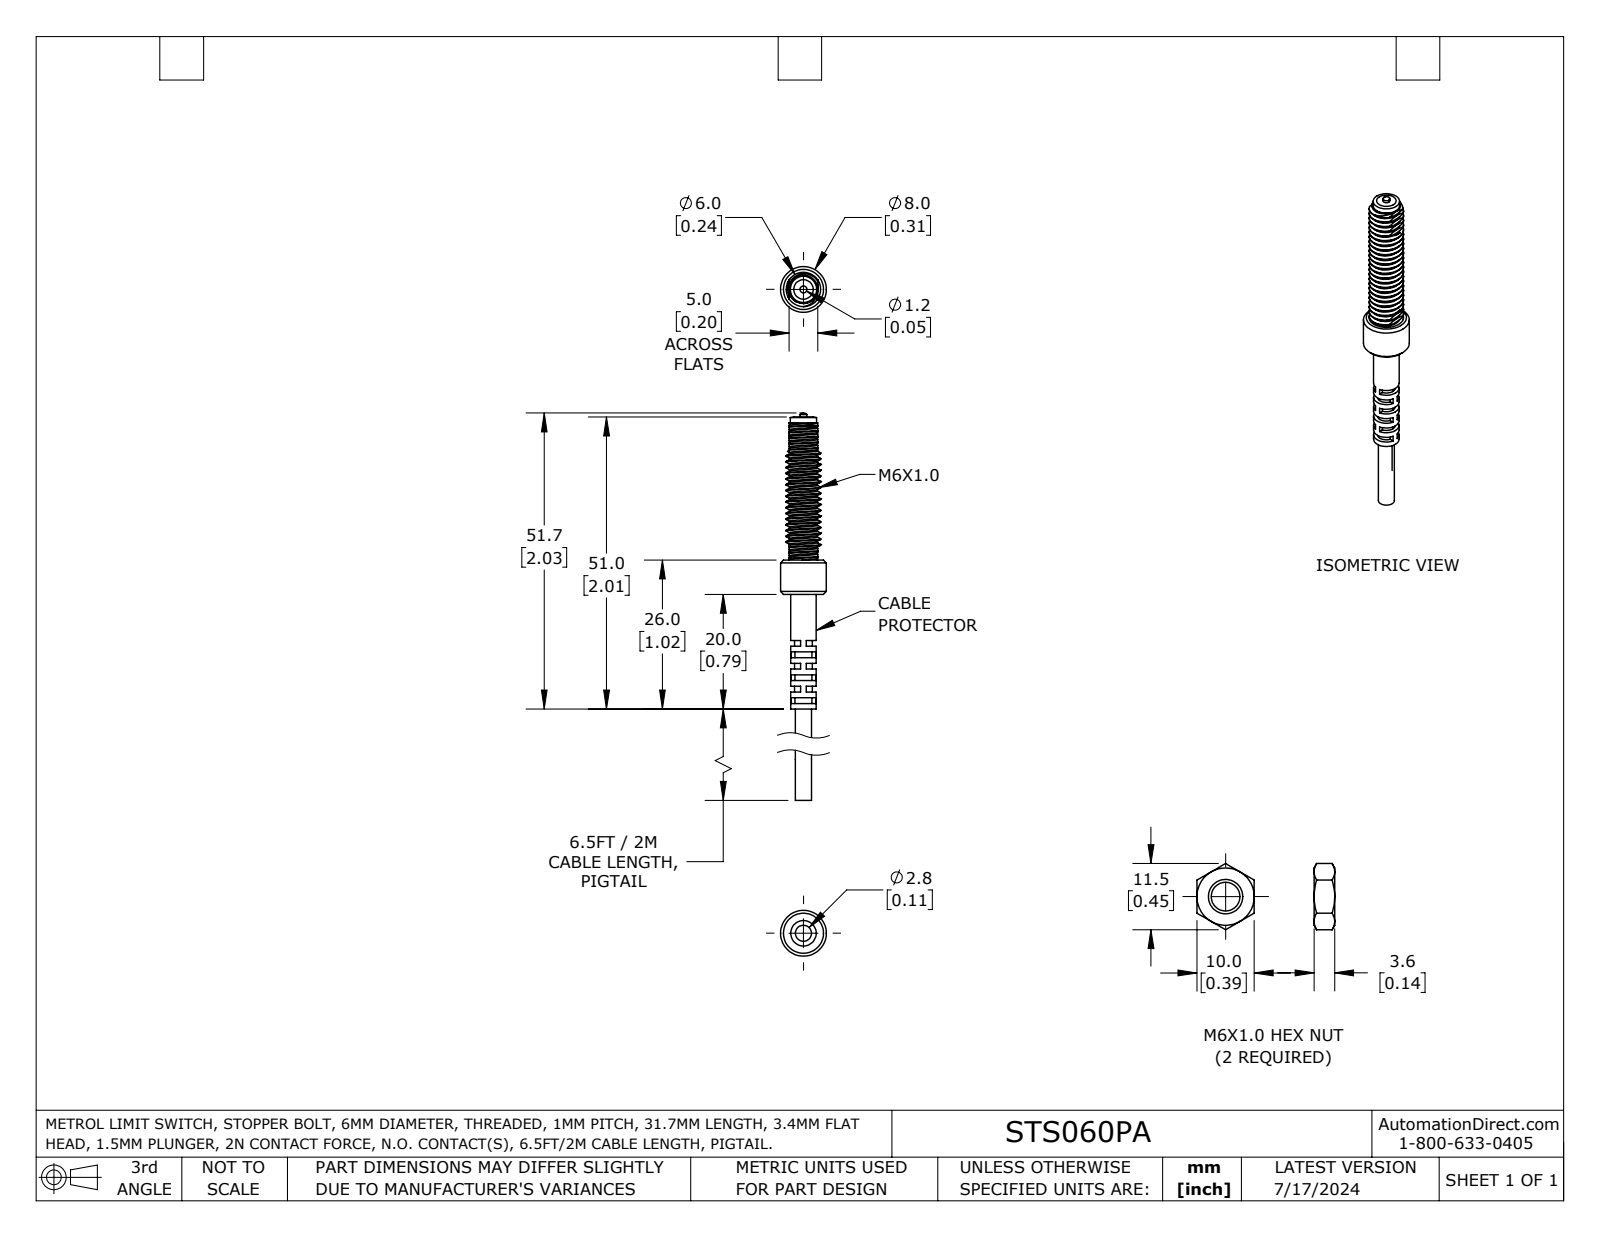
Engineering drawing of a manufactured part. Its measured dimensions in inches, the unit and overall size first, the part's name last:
Units: inches
Overall size (bounding box): 2.27 × 0.315 × 0.315
Round bosses / shafts (diameter × count): ⌀0.315 ×1, ⌀0.236 ×1, ⌀0.181 ×1, ⌀0.175 ×1, ⌀0.122 ×1, ⌀0.11 ×1, ⌀0.047 ×1
Main face-to-face distances: 0.039, 0.079, 0.118, 0.197, 0.236, 0.157, 0.276, 0.315, 0.354, 1.024
Volume: 0.07 in³ · Surface area: 2.097 in²
Bodies: 1 solid, 168 faces (77 planar, 76 cylindrical, 15 other)
Part name (STEP PRODUCT): STS060PA
STEP written by: SolidWorks 2023 (AUTOMOTIVE_DESIGN)
